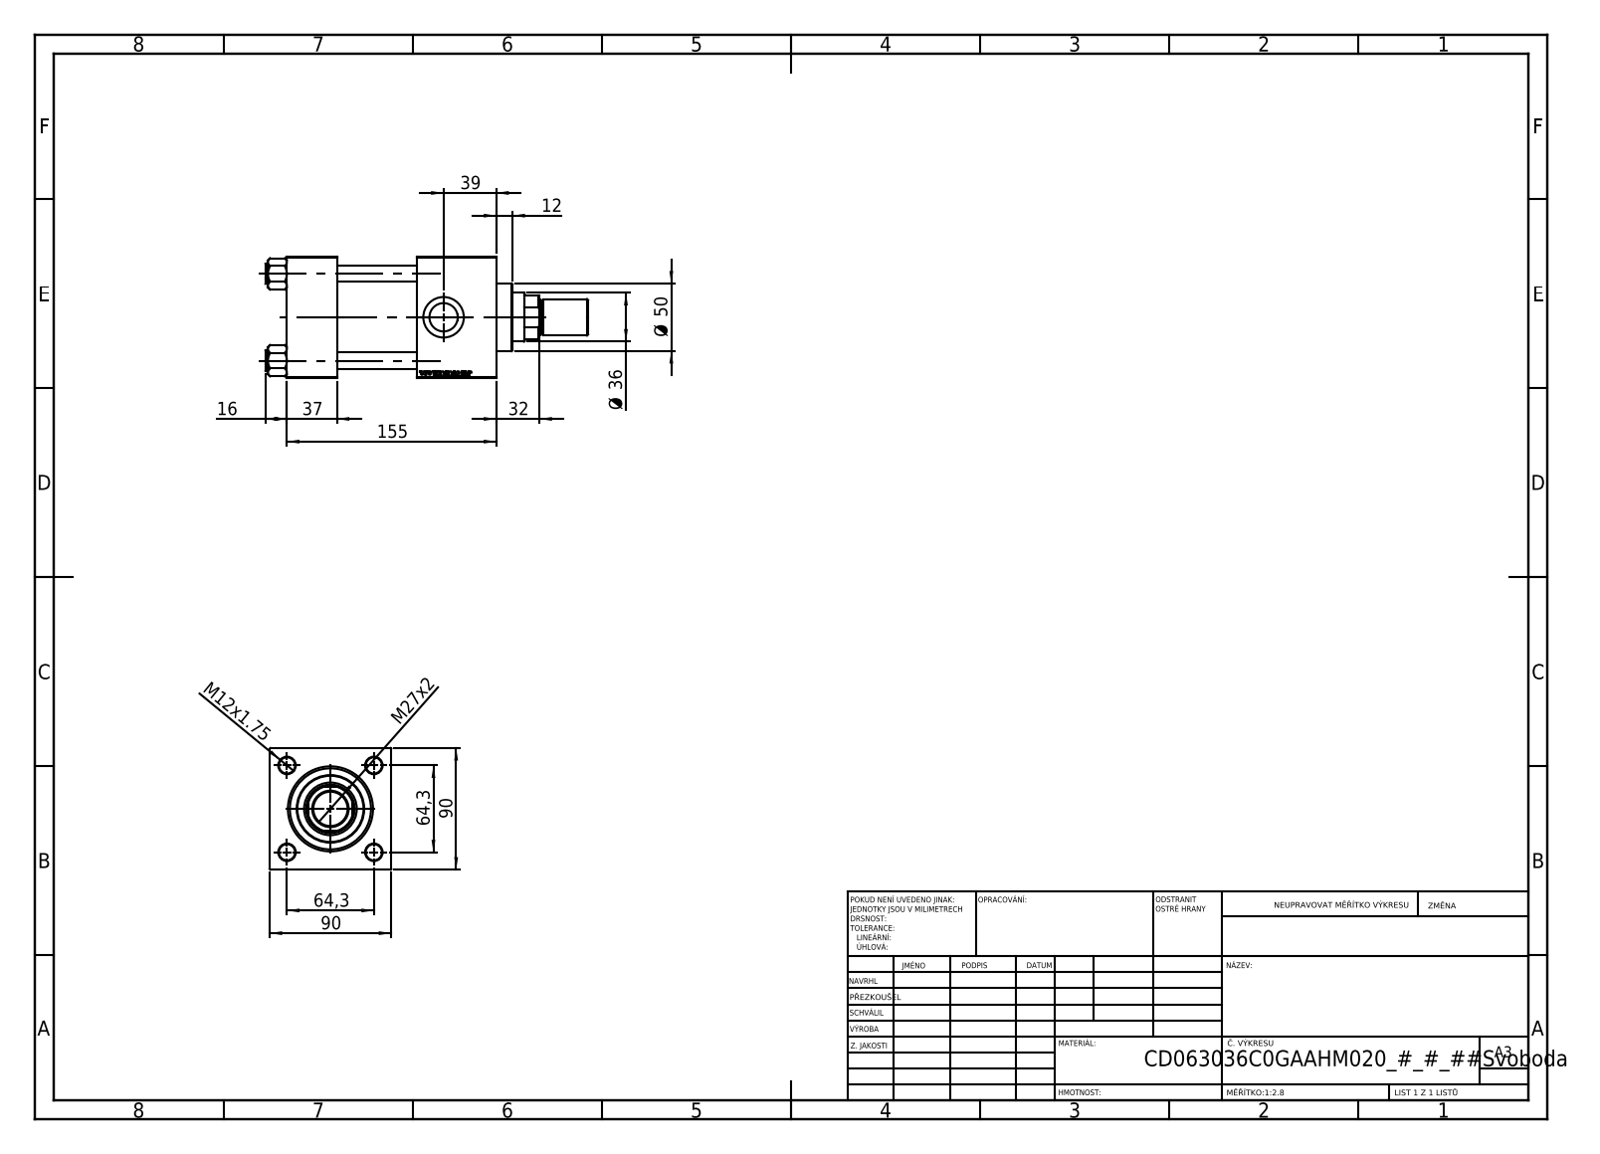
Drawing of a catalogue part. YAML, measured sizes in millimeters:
part_name: "V215CD_C_TYCINKA; V215CD_Body_C; V215CD_VC_C; NUT_M5_V215CD_C (+2 more)"
step_written_by: "SolidWorks 2019 (CONFIG_CONTROL_DESIGN)"
units: millimeters
bodies: {solids: 12, faces: 1163, planar: 530, cylindrical: 91, other: 542}
overall_size: [239, 90, 90]
volume: 988249
surface_area: 188505
round_holes:
  - {diameter: 12, count: 4}
  - {diameter: 7, count: 2}
  - {diameter: 20.96, count: 2}
  - {diameter: 30, count: 2}
  - {diameter: 25.5, count: 1}
  - {diameter: 36, count: 1}
  - {diameter: 39, count: 1}
  - {diameter: 50, count: 1}
  - {diameter: 60, count: 1}
  - {diameter: 63, count: 1}
round_bosses_or_shafts:
  - {diameter: 15, count: 4}
  - {diameter: 69, count: 1}
  - {diameter: 27, count: 1}
  - {diameter: 25, count: 1}
partial_cylinders:
  - {radius: 17.5, count: 1}
face_to_face_distances: [90, 59, 37, 155, 118, 96, 20, 126.3, 89.3, 30.3]
hole_center_spacings: [45.47, 64.3, 90.93]
